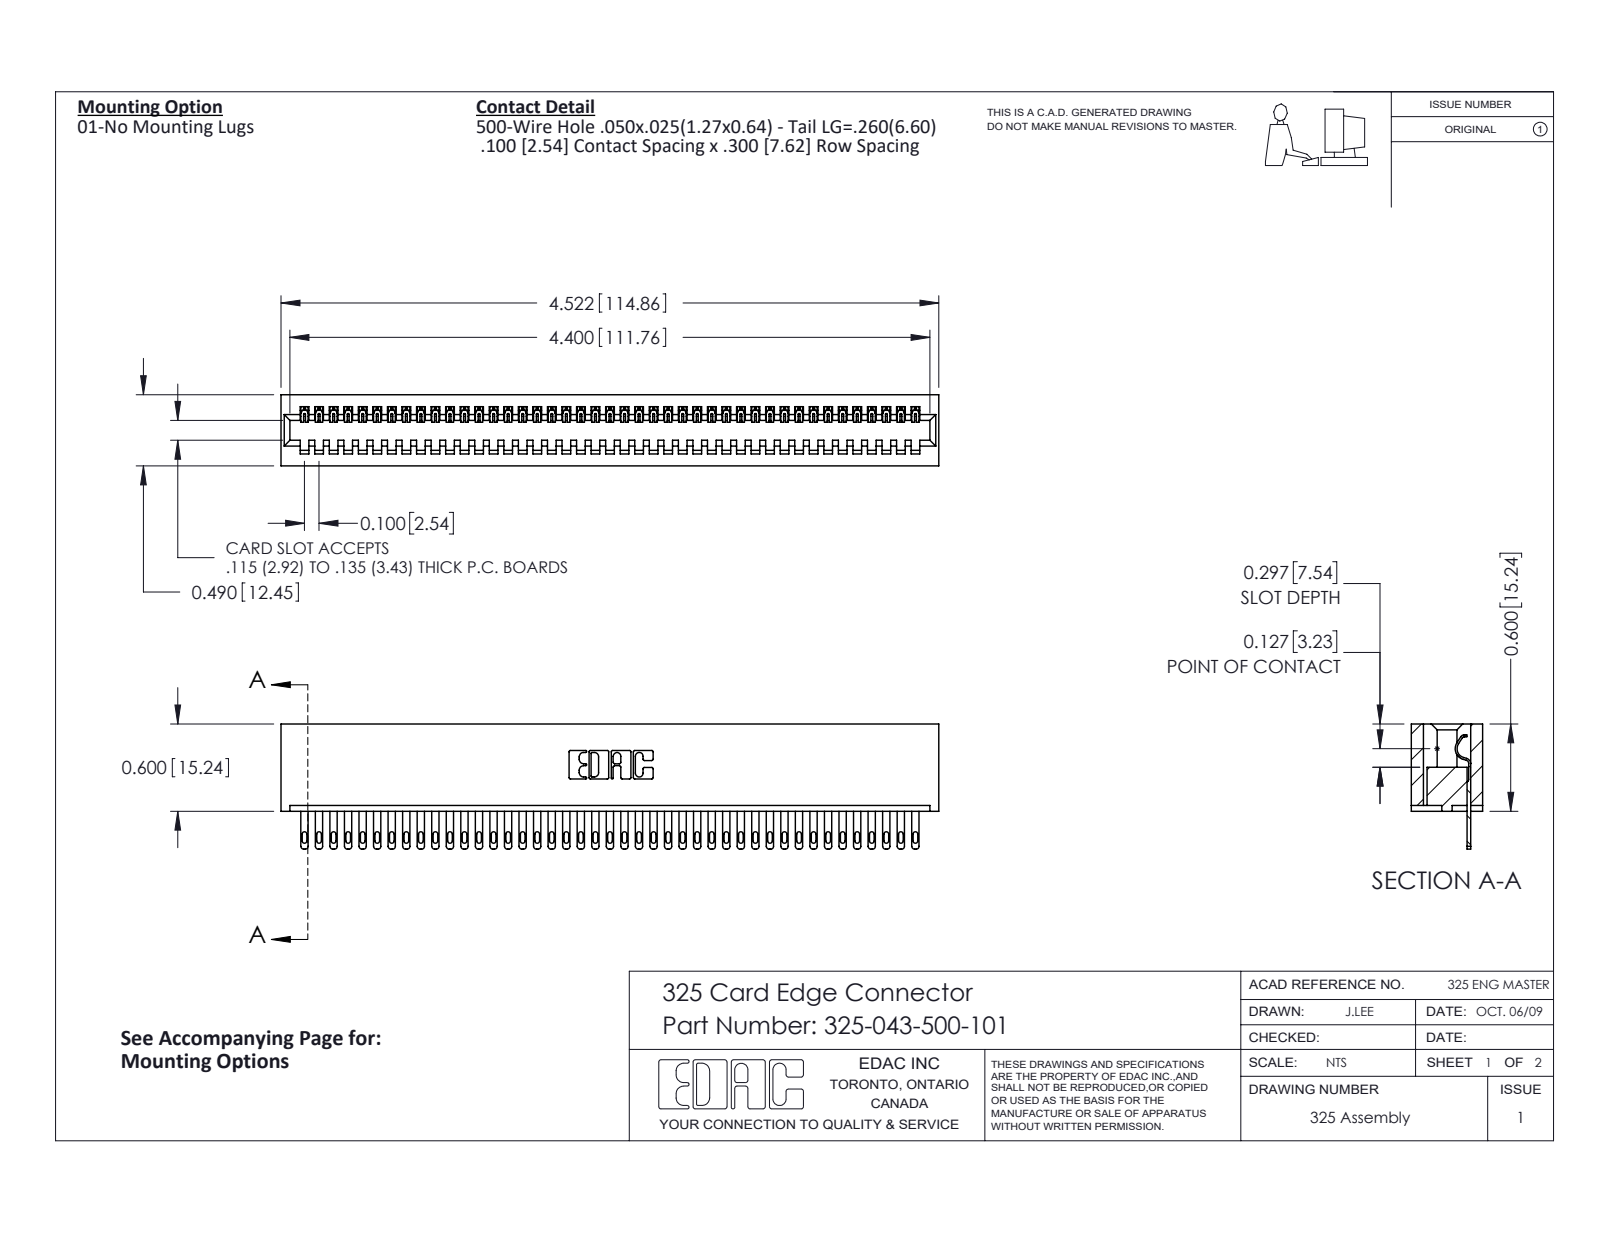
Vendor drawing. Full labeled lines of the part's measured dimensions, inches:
Part name (STEP PRODUCT): 325-043-500-101; 325-292-001_325-293-100; 325 Part_Lugless
STEP written by: SolidWorks 2016 (CONFIG_CONTROL_DESIGN)
Units: inches
Bodies: 44 solids, 2428 faces (1614 planar, 814 cylindrical, 0 other)
Overall size (bounding box): 4.522 × 0.86 × 0.49
Volume: 0.927 in³ · Surface area: 26.66 in²
Partial cylindrical surfaces — rounded edges, fillets, slot ends (radius × count): R0.006 ×86, R0.016 ×86, R0.02 ×86, R0.01 ×22, R0.007 ×6, R0.031 ×6, R0.026 ×3, R0.014 ×1
Main face-to-face distances: 0.083, 0.407, 0.3, 0.49, 0.107, 0.383, 0.025, 0.325, 0.56, 0.263
